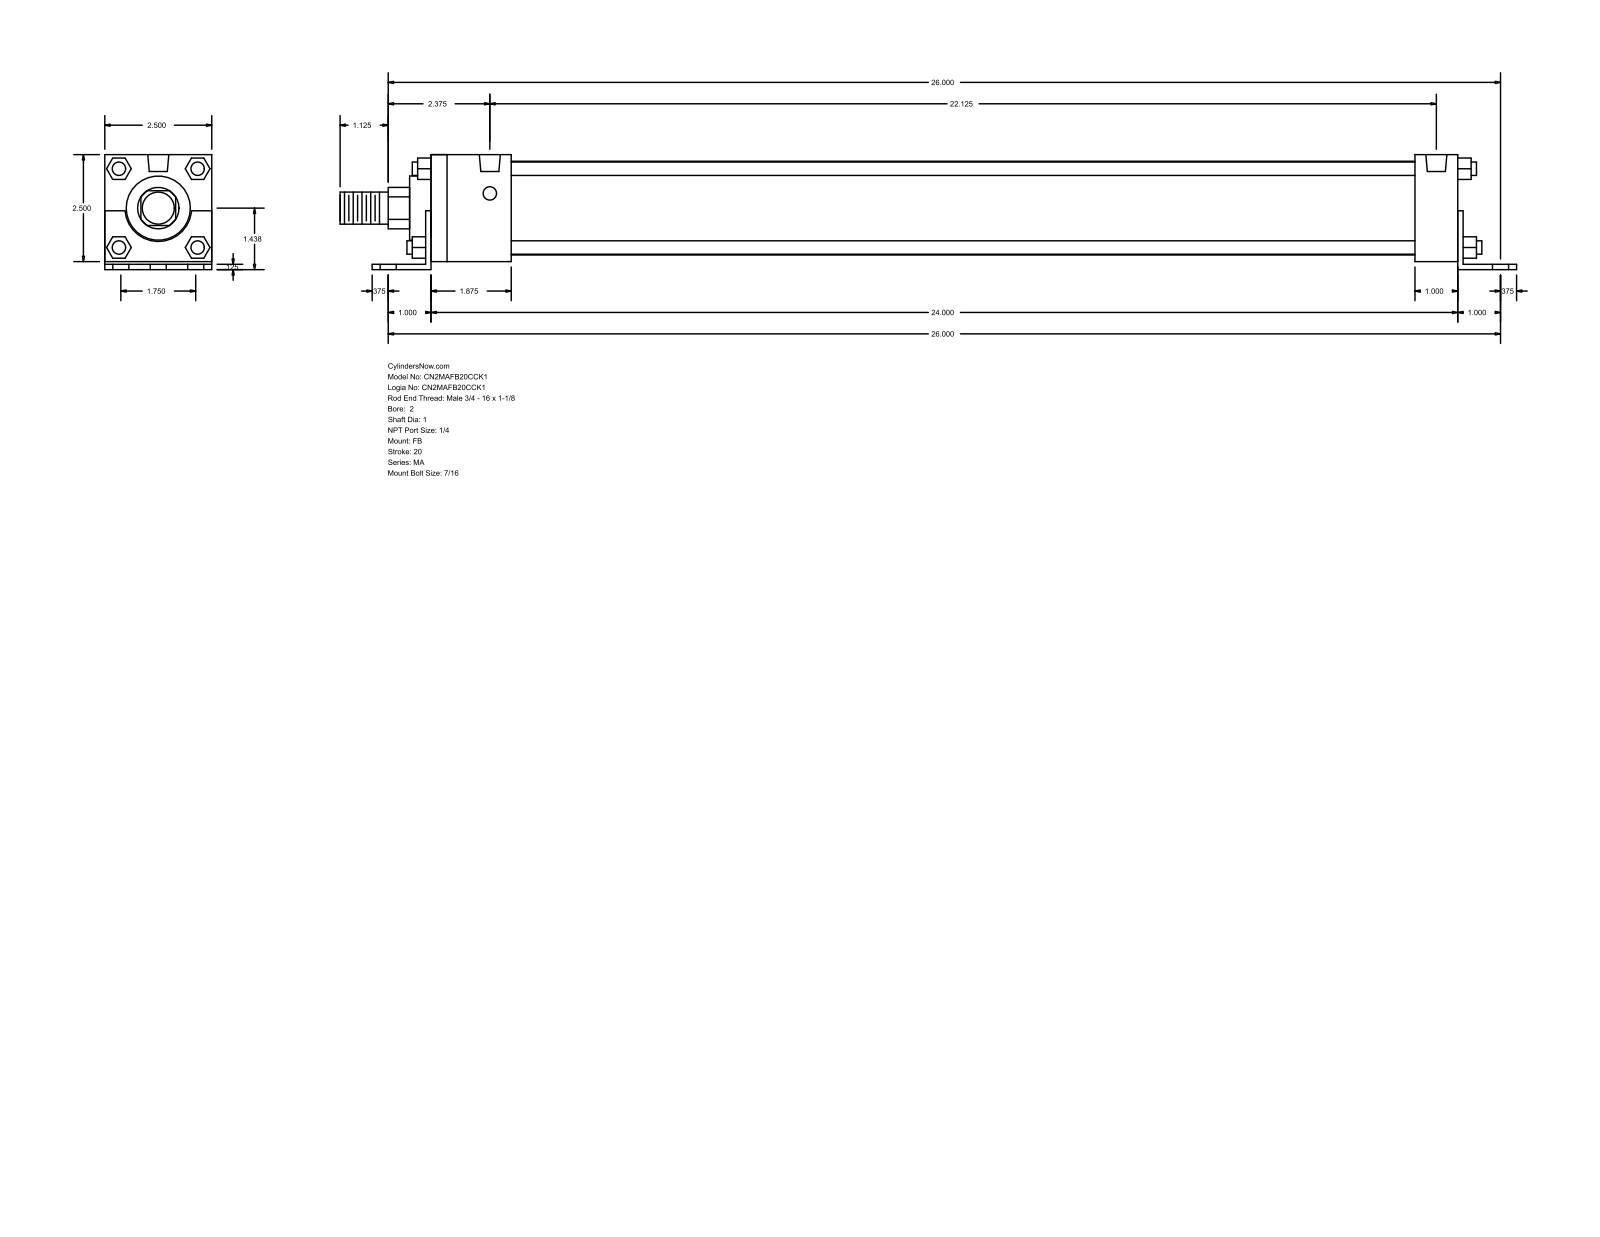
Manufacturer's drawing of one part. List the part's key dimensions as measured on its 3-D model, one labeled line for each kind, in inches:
Part name (STEP PRODUCT): MA_FB__0200_1
STEP written by: GSSL Pune (CONFIG_CONTROL_DESIGN)
Units: inches
Bodies: 0 solids, 140 faces (105 planar, 35 cylindrical, 0 other)
Overall size (bounding box): 27.5 × 2.687 × 2.5
Round holes (diameter × count): ⌀0.437 ×6, ⌀0.313 ×4, ⌀0.492 ×2
Round bosses / shafts (diameter × count): ⌀0.313 ×4, ⌀2.19 ×1, ⌀1.5 ×1, ⌀1 ×1, ⌀0.75 ×1
Partial cylindrical surfaces — rounded edges, fillets, slot ends (radius × count): R0.484 ×1, R0.78 ×1
Main face-to-face distances: 2.5, 0.125, 0.187, 2.687, 0.063, 2.563, 24.125, 0.5, 24, 1.125
Hole centre spacings: 0.875, 26.015, 26, 1.737, 1.75, 2.531, 22.125, 23.641
